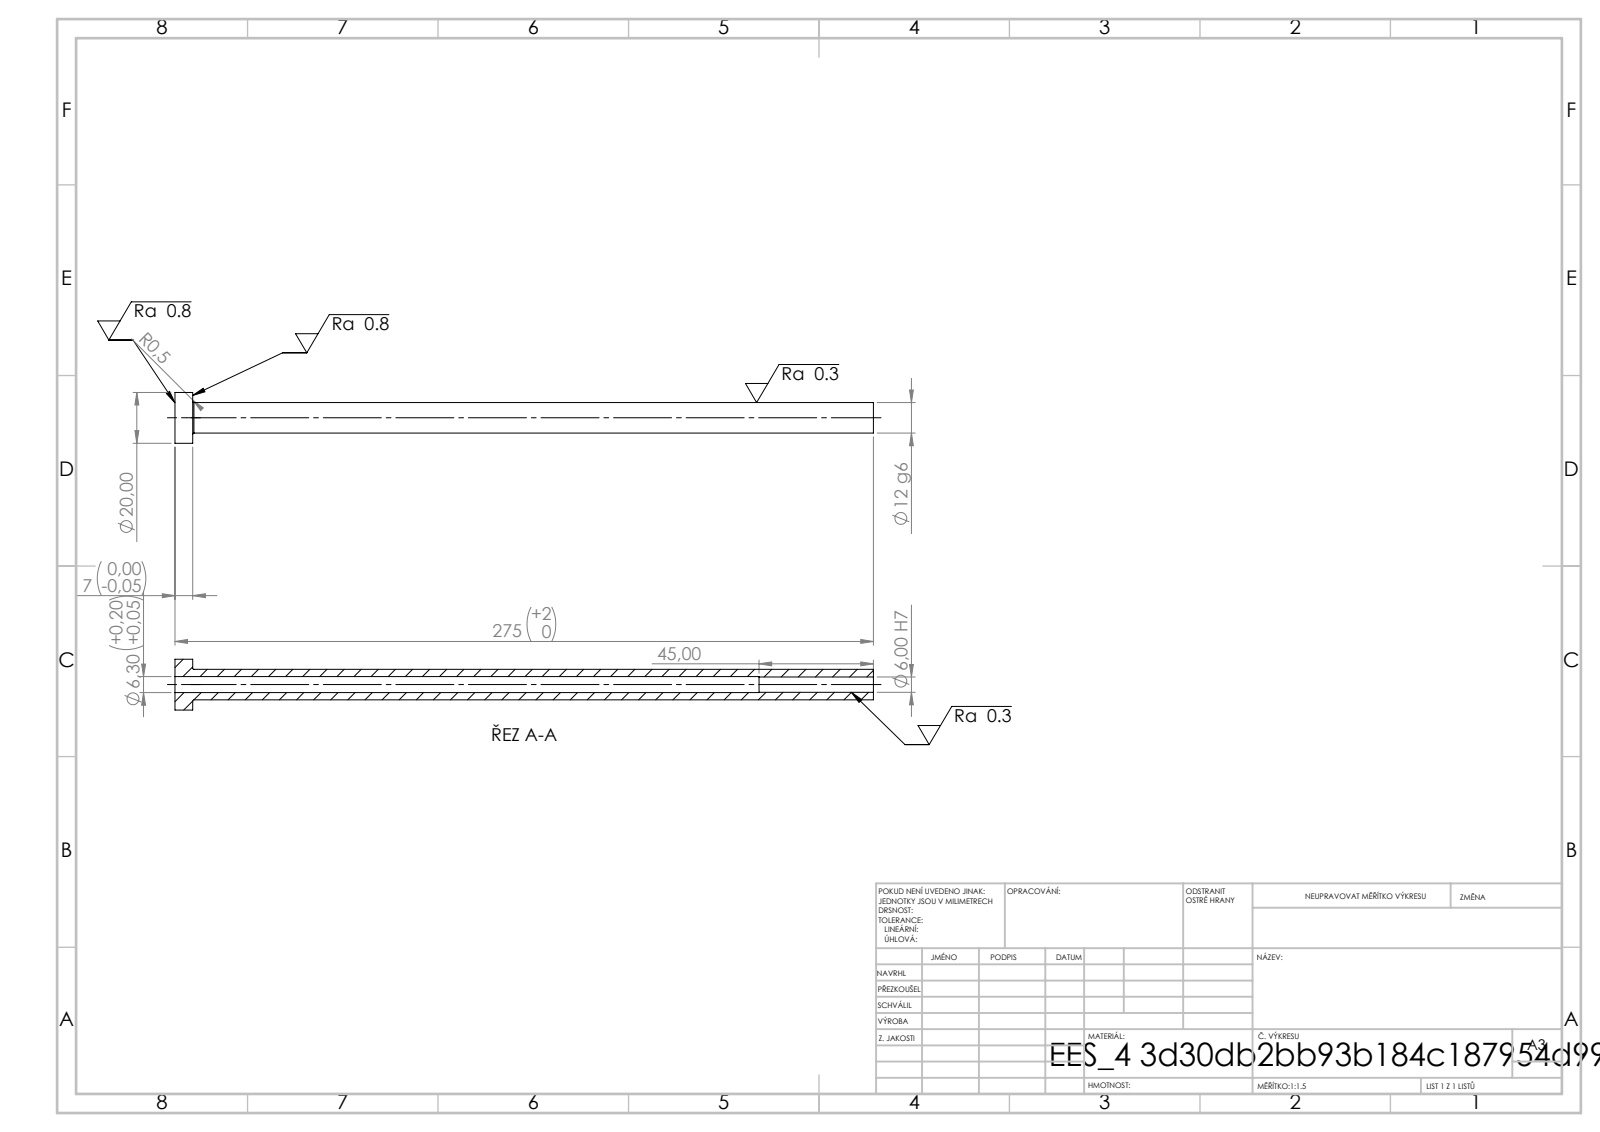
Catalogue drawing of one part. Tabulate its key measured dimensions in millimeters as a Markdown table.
| quantity | value |
| --- | --- |
| STEP written by | SolidWorks 2019 (CONFIG_CONTROL_DESIGN) |
| units | millimeters |
| bodies | 1 solid, 14 faces (4 planar, 8 cylindrical, 2 other) |
| overall size | 275 × 20 × 20 |
| volume | 24 069 mm³ |
| surface area | 16 507 mm² |
| round holes (diameter × count) | 6 × 1, 6.3 × 1 |
| round bosses / shafts (diameter × count) | 20 × 1, 12 × 1 |
| main face-to-face distances | 7, 275, 268, 230, 223, 45 |
